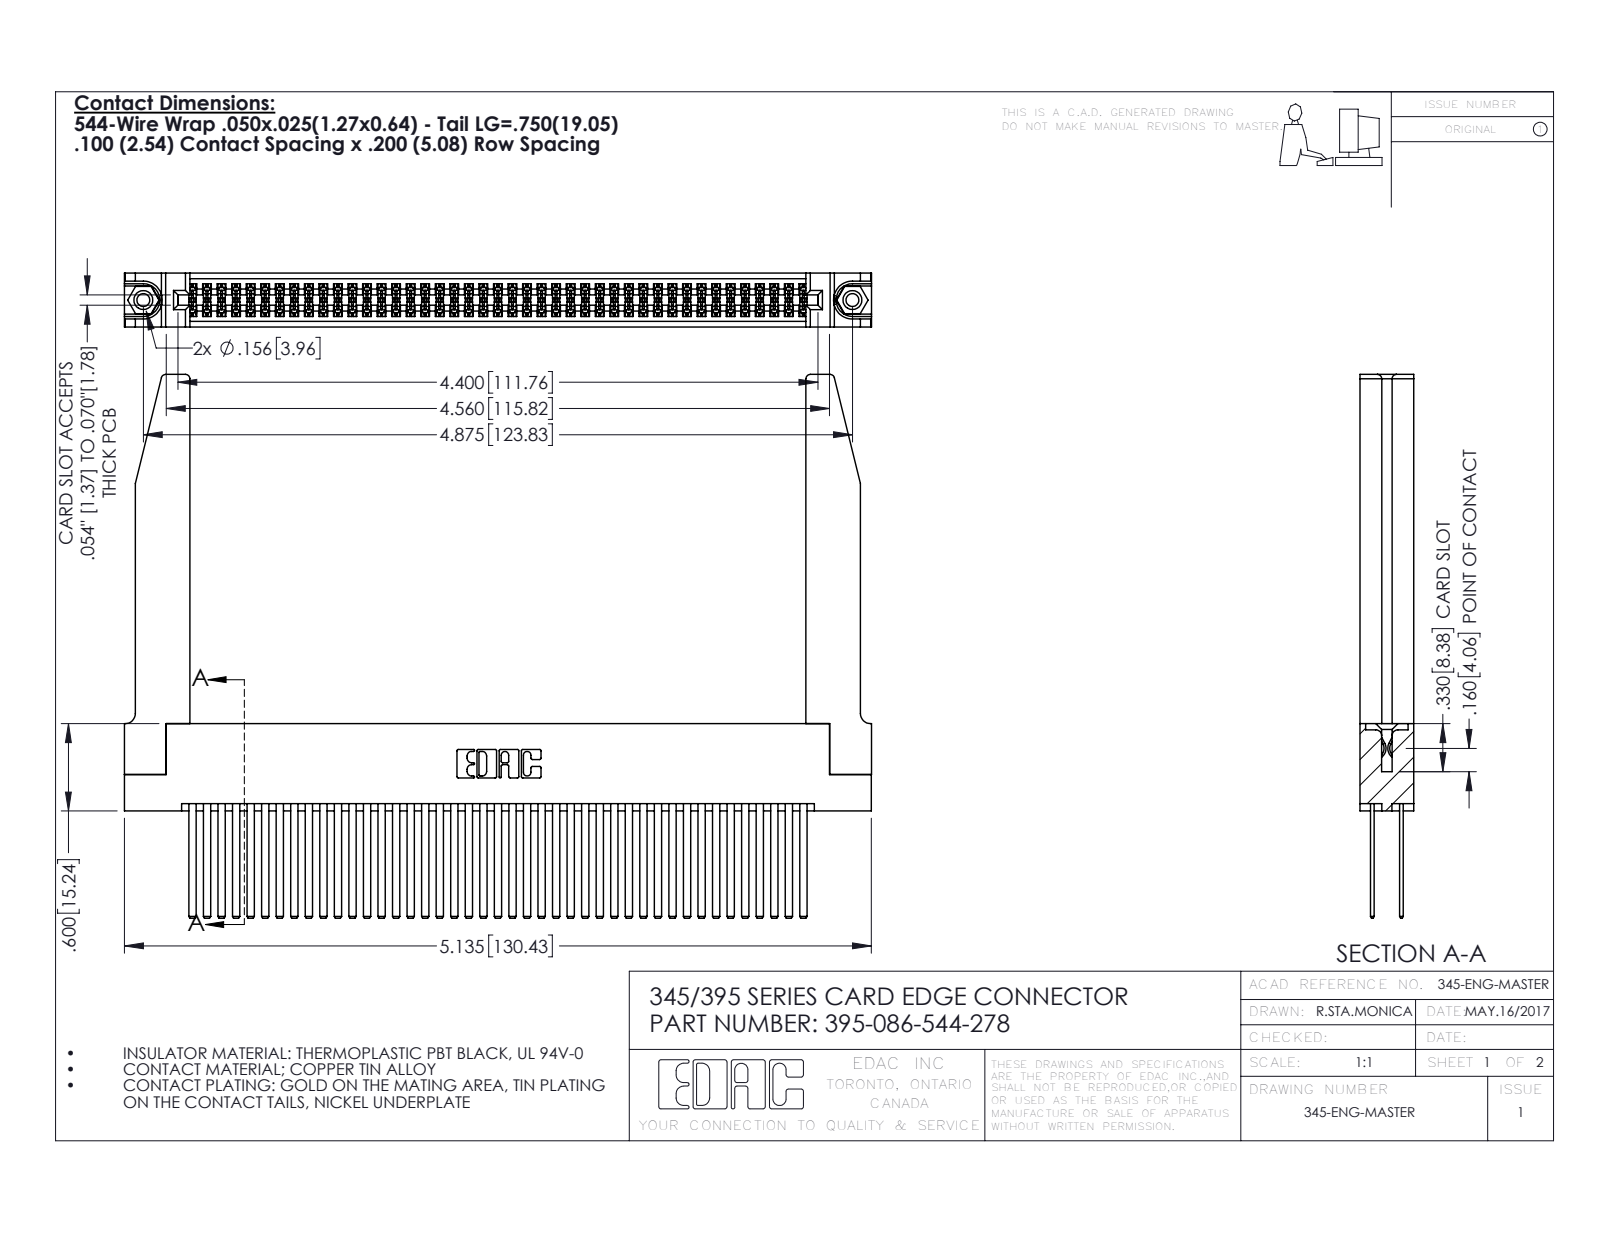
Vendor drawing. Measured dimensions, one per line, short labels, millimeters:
name: 345 Part_Flush Mounting Lugs - 0.156 Dia-TH; 345-220-078_345-220-078; 345-292-001_345-293-144; 345-250-001_345-250-001-102 (+1 more)
written by: SolidWorks 2016 (CONFIG_CONTROL_DESIGN)
unit: mm
bodies: 91 solids, 4144 faces (2716 planar, 1376 cylindrical, 52 other)
size: 130.5 × 94.9 × 9.4
volume: 21 660 mm³; area: 30 920 mm²
holes: 2× ⌀2.3, 2× ⌀3.2, 2× ⌀4, 1× ⌀1.6
bosses: 2× ⌀3.9
rounds: 129× R0.2, 22× R0.3, 8× R0.8, 6× R0.2, 6× R0.8, 3× R0.7, 2× R0.4, 2× R0.5
face distances: 1.8, 7.6, 5.1, 2.5, 6.9, 0.6, 9.4, 5.7, 4.4, 3.8
hole spacings: 6.9, 117.8, 123.8
